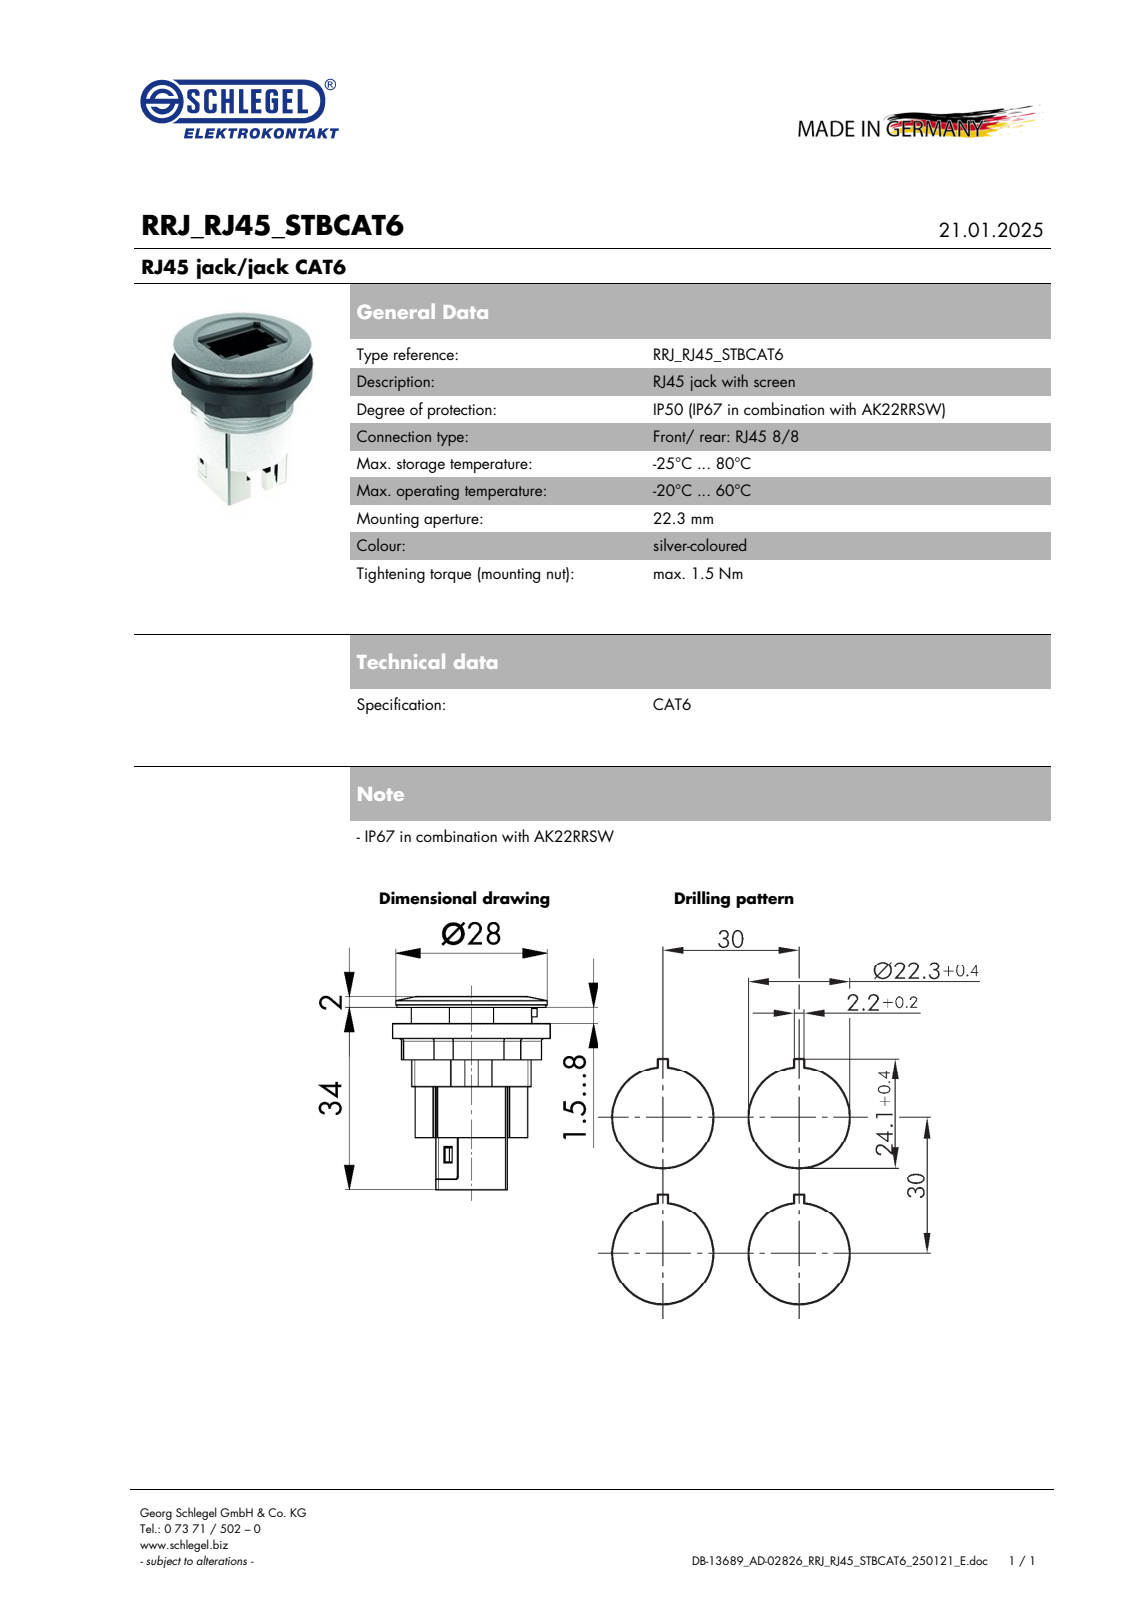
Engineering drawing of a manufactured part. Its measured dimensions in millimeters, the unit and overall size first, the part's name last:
Units: millimetres
Overall size (bounding box): 35.6 × 29 × 29
Round holes (diameter × count): ⌀0.65 ×16, ⌀1.25 ×4, ⌀18.5 ×1, ⌀20.05 ×1, ⌀20.92 ×1, ⌀22.6 ×1, ⌀25.35 ×1
Round bosses / shafts (diameter × count): ⌀1.2 ×4, ⌀29 ×1, ⌀27.9 ×1, ⌀27.4 ×1, ⌀22 ×1, ⌀20.7 ×1
Partial cylindrical surfaces — rounded edges, fillets, slot ends (radius × count): R0.3 ×60, R0.5 ×48, R1 ×10, R0.2 ×8, R0.8 ×8, R1.05 ×8, R0.35 ×6, R0.4 ×6
Main face-to-face distances: 0.8, 15.6, 15.7, 13.15, 3, 10.15, 4.6, 0.5, 13.23, 6.2
Hole centre spacings: 1.02, 20.28, 2.04, 20.35, 3.06, 20.48, 4.08, 20.25
Volume: 9 165 mm³ · Surface area: 13 898 mm²
Bodies: 5 solids, 1572 faces (1098 planar, 378 cylindrical, 96 other)
Part name (STEP PRODUCT): Bauteil3252
STEP written by: Autodesk Inventor 2023 (AUTOMOTIVE_DESIGN)
